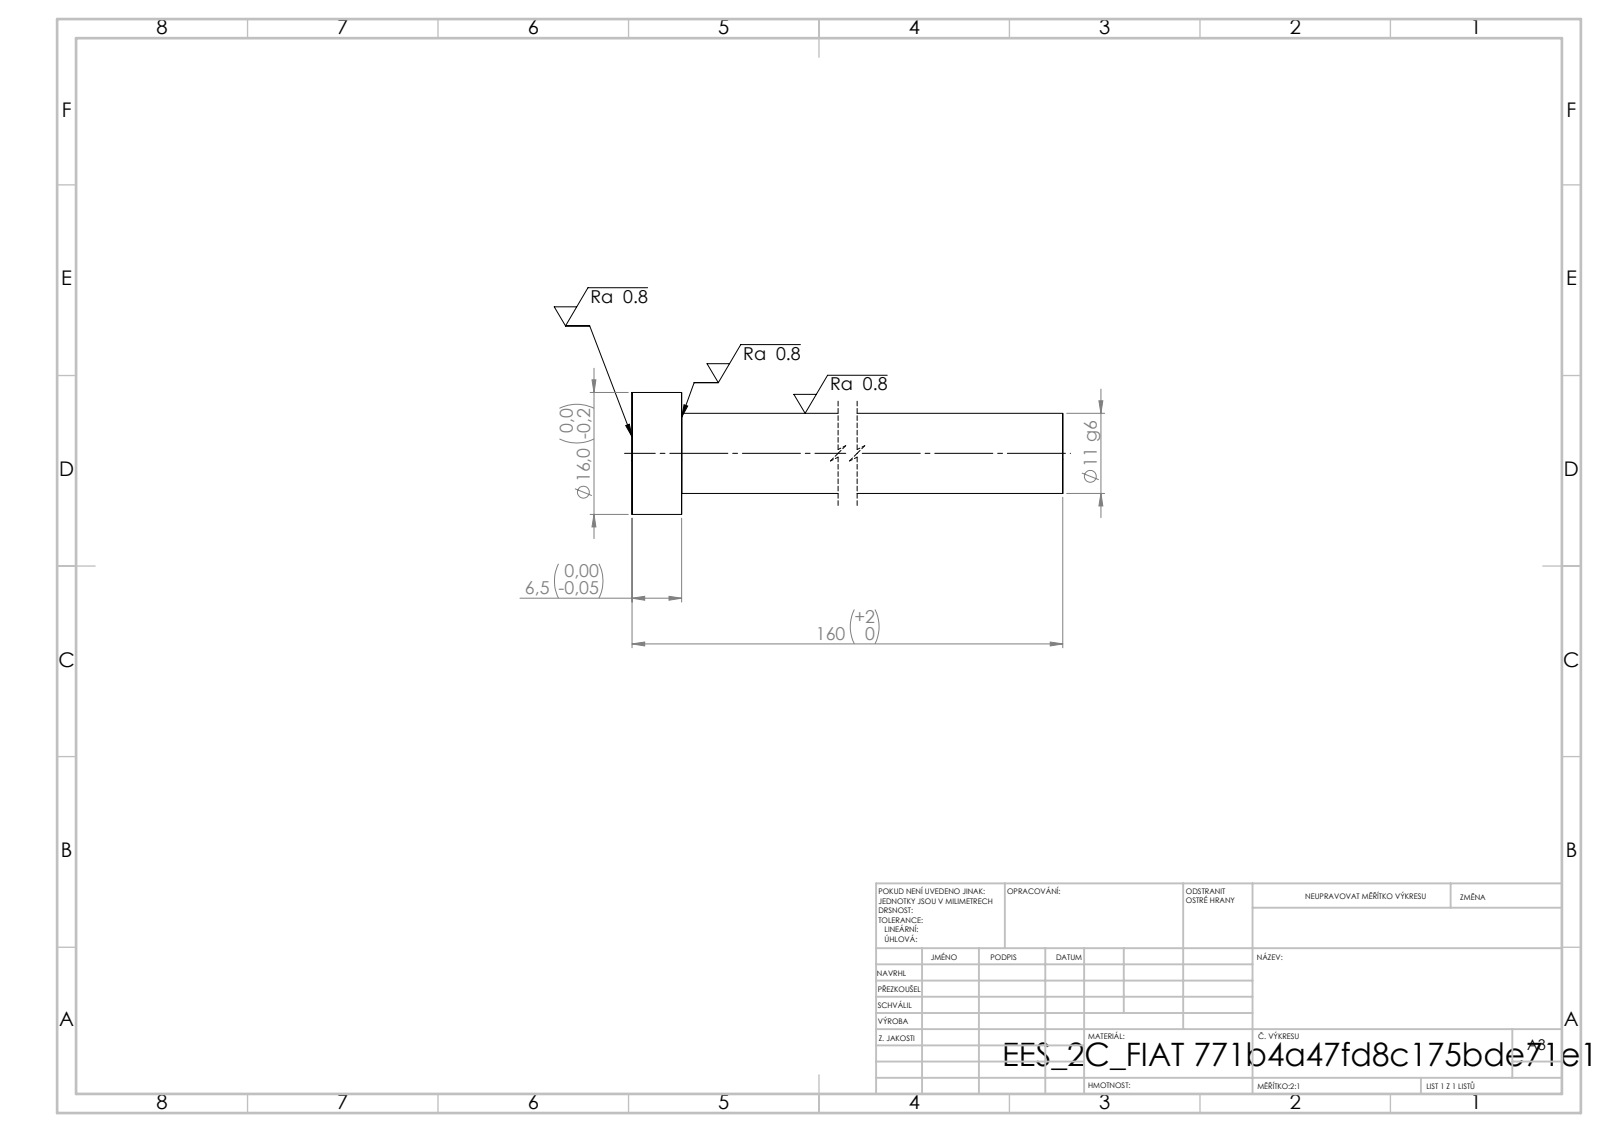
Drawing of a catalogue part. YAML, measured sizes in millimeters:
step_written_by: "SolidWorks 2019 (CONFIG_CONTROL_DESIGN)"
units: millimeters
bodies: {solids: 1, faces: 7, planar: 3, cylindrical: 4, other: 0}
overall_size: [160, 16, 16]
volume: 14598
surface_area: 5792
round_bosses_or_shafts:
  - {diameter: 16, count: 1}
  - {diameter: 10.5, count: 1}
face_to_face_distances: [6.5, 160, 153.5]
